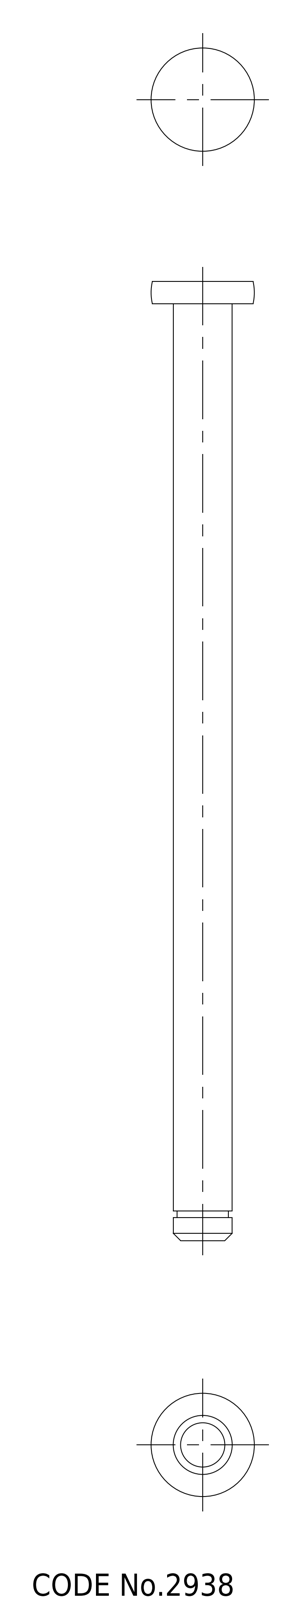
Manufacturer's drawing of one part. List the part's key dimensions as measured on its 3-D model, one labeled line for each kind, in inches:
Part name (STEP PRODUCT): shaft; TH_121_8_127
STEP written by: SolidWorks 2015 (AUTOMOTIVE_DESIGN)
Units: inches
Bodies: 1 solid, 15 faces (5 planar, 6 cylindrical, 4 other)
Overall size (bounding box): 5.118 × 0.551 × 0.551
Volume: 0.416 in³ · Surface area: 5.614 in²
Round bosses / shafts (diameter × count): ⌀0.315 ×1, ⌀0.276 ×1
Main face-to-face distances: 0.118, 5, 5.118, 0.157, 4.843, 4.961, 0.122, 0.035, 4.878, 4.996
